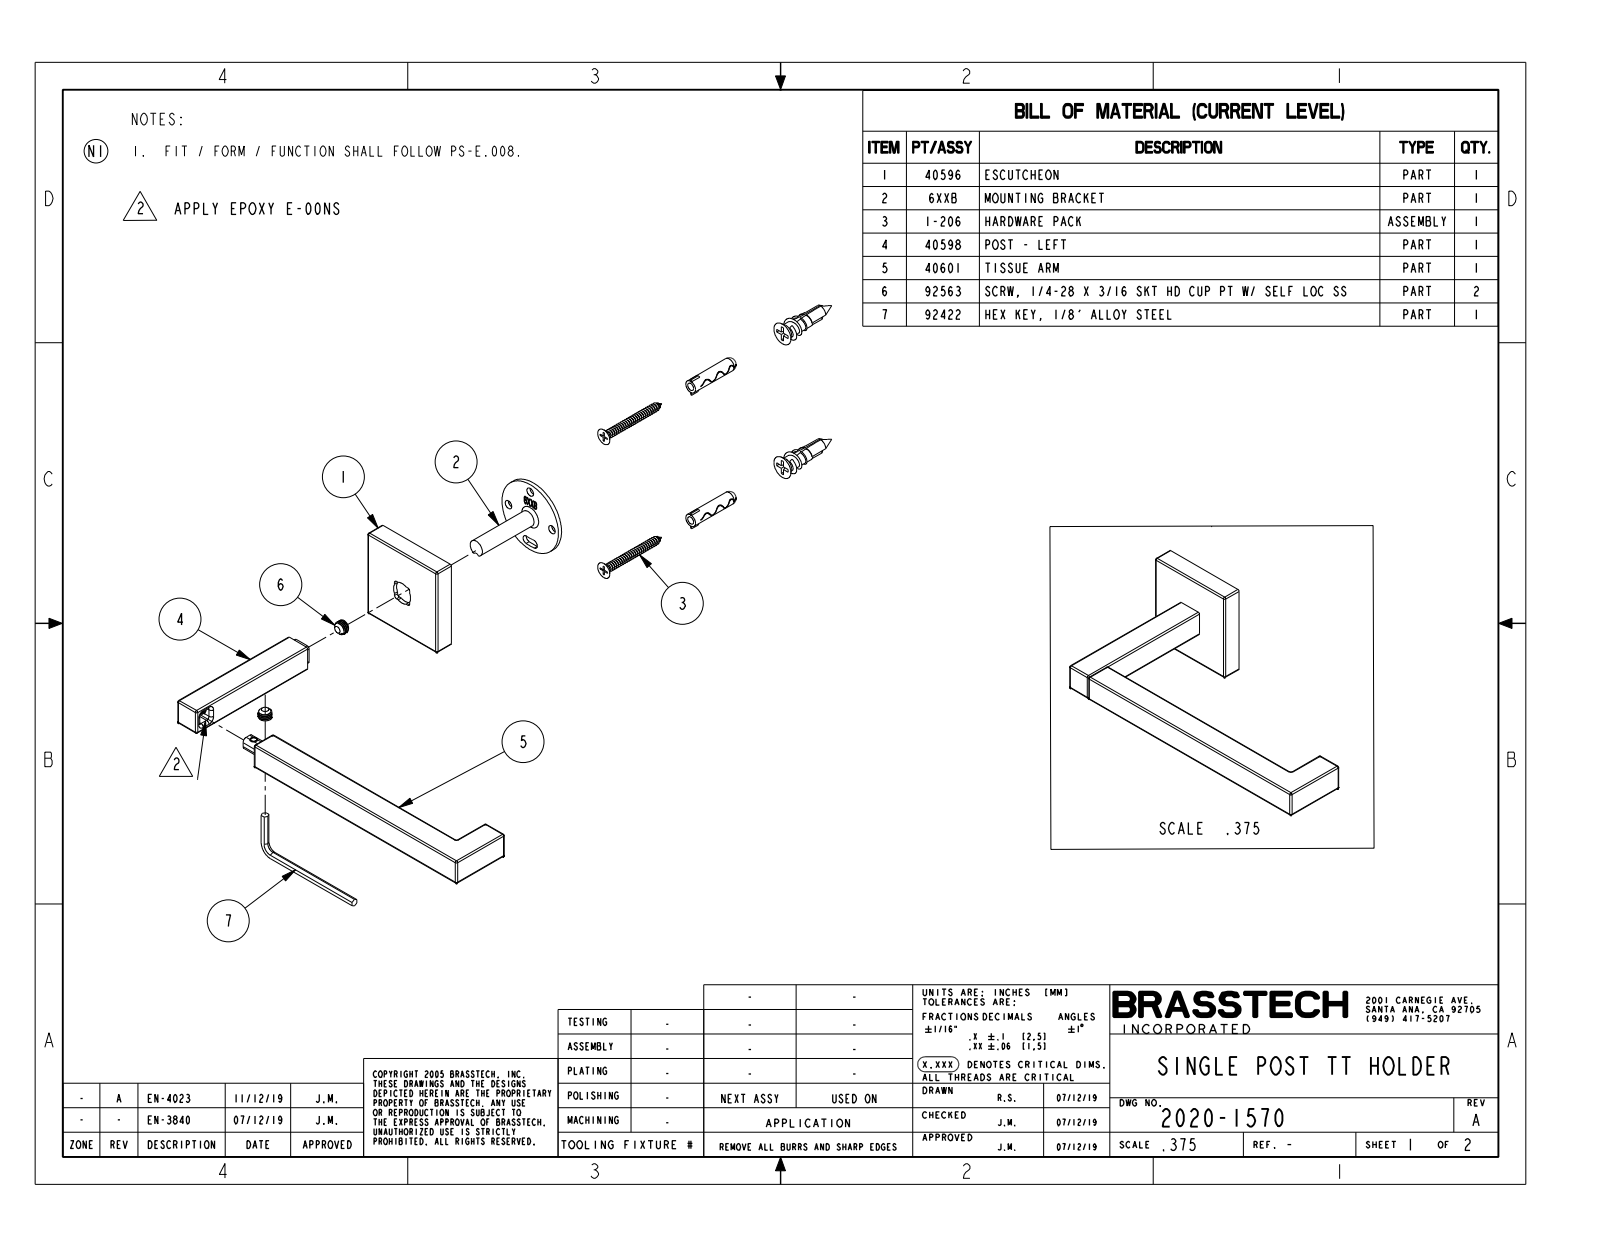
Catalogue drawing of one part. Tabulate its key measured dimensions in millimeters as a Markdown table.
| quantity | value |
| --- | --- |
| part name | 2020-1570 |
| STEP written by | CREO PARAMETRIC BY PTC INC, 2018400 (AUTOMOTIVE_DESIGN) |
| units | millimeters |
| bodies | 1 solid, 73 faces (19 planar, 34 cylindrical, 20 other) |
| overall size | 162.6 × 82.7 × 45.7 |
| volume | 56 110 mm³ |
| surface area | 17 030 mm² |
| partial cylindrical surfaces (radius × count) | 0.8 × 34 |
| main face-to-face distances | 12.7, 9.5, 16.5, 29.2, 82.7, 73.2, 70, 60.5, 45.7, 133.4 |
